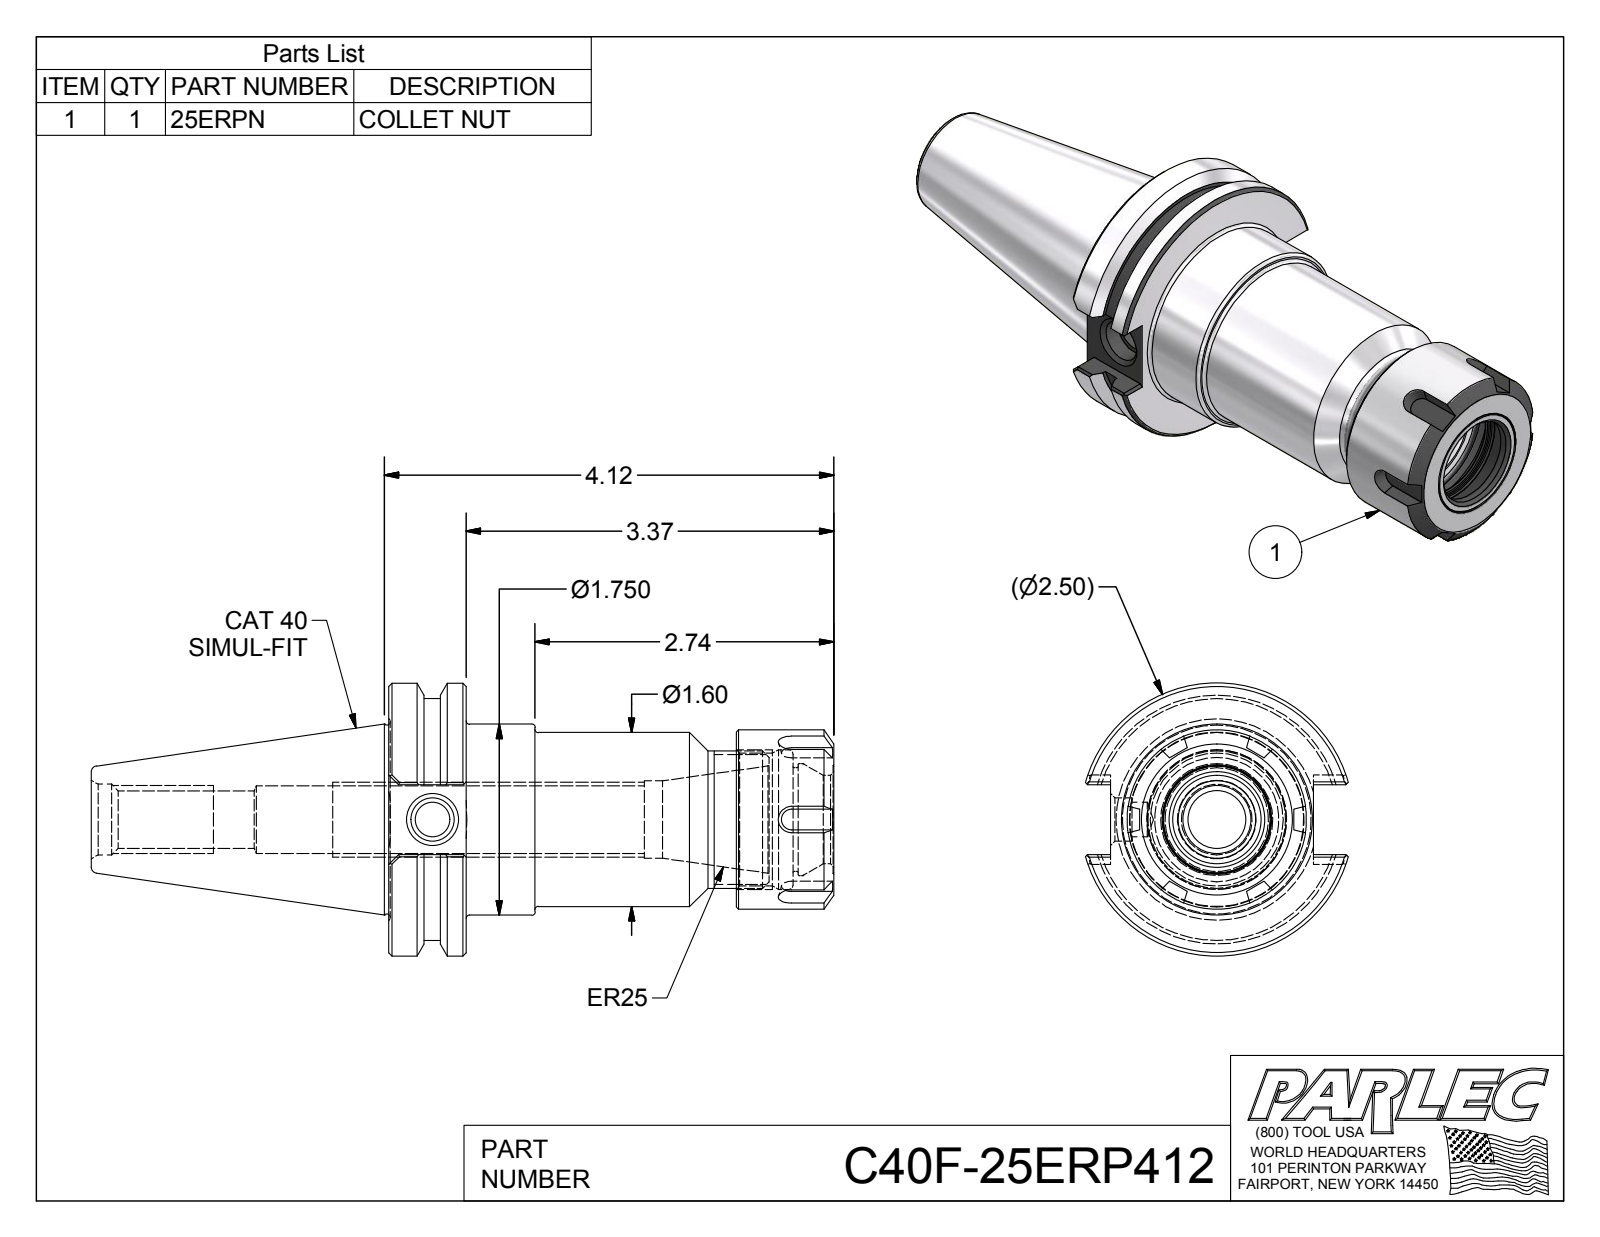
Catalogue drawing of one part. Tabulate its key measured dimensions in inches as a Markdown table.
| quantity | value |
| --- | --- |
| part name | C40F-25ER4-1; 25ERPN; C40F-25ERP412 |
| STEP written by | Autodesk Inventor 2016 (AUTOMOTIVE_DESIGN) |
| units | inches |
| bodies | 2 solids, 125 faces (56 planar, 21 cylindrical, 48 other) |
| overall size | 6.807 × 2.5 × 2.406 |
| volume | 11.27 in³ |
| surface area | 61.66 in² |
| round holes (diameter × count) | 0.315 × 1, 0.399 × 1, 0.527 × 1, 0.62 × 1, 0.648 × 1, 0.71 × 1, 0.811 × 1, 0.95 × 1, 1.027 × 1, 1.217 × 1, 1.28 × 1 |
| round bosses / shafts (diameter × count) | 2.5 × 1, 2.215 × 1, 1.75 × 1, 1.643 × 1, 1.595 × 1, 1.26 × 1 |
| main face-to-face distances | 0.71, 4.08, 3.37, 3.187, 2.477, 0.893, 3.705, 2.995, 0.518, 0.375 |
